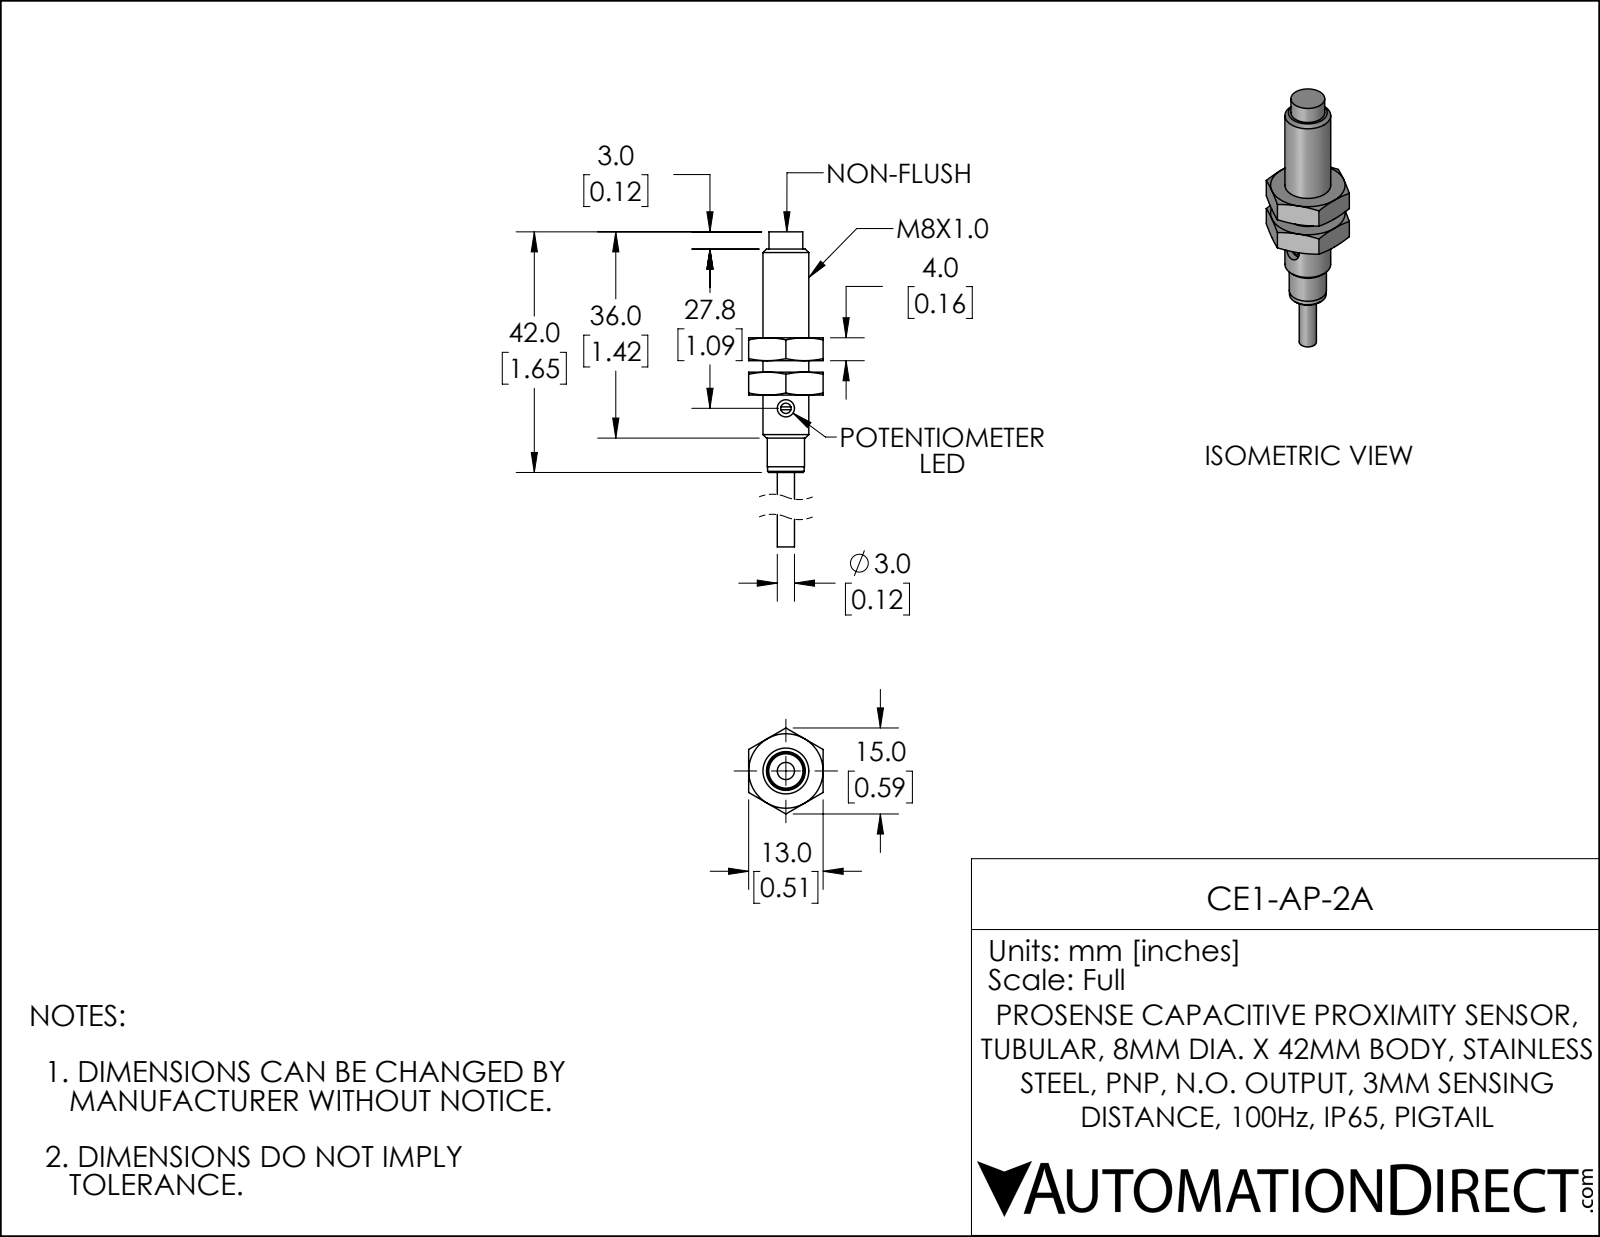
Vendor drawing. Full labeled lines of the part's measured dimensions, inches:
Part name (STEP PRODUCT): CE1-AP-2A
STEP written by: SolidWorks 2019 (CONFIG_CONTROL_DESIGN)
Units: inches
Bodies: 3 solids, 68 faces (28 planar, 9 cylindrical, 31 other)
Overall size (bounding box): 2.047 × 0.591 × 0.512
Volume: 0.174 in³ · Surface area: 3.281 in²
Round holes (diameter × count): ⌀0.118 ×1, ⌀0.272 ×1
Round bosses / shafts (diameter × count): ⌀0.315 ×1, ⌀0.256 ×1, ⌀0.252 ×1, ⌀0.232 ×1, ⌀0.118 ×1, ⌀0.071 ×1
Main face-to-face distances: 0.512, 0.236, 0.157, 0.394, 0.079, 0.926, 0.728, 0.885, 0.964, 1.122
